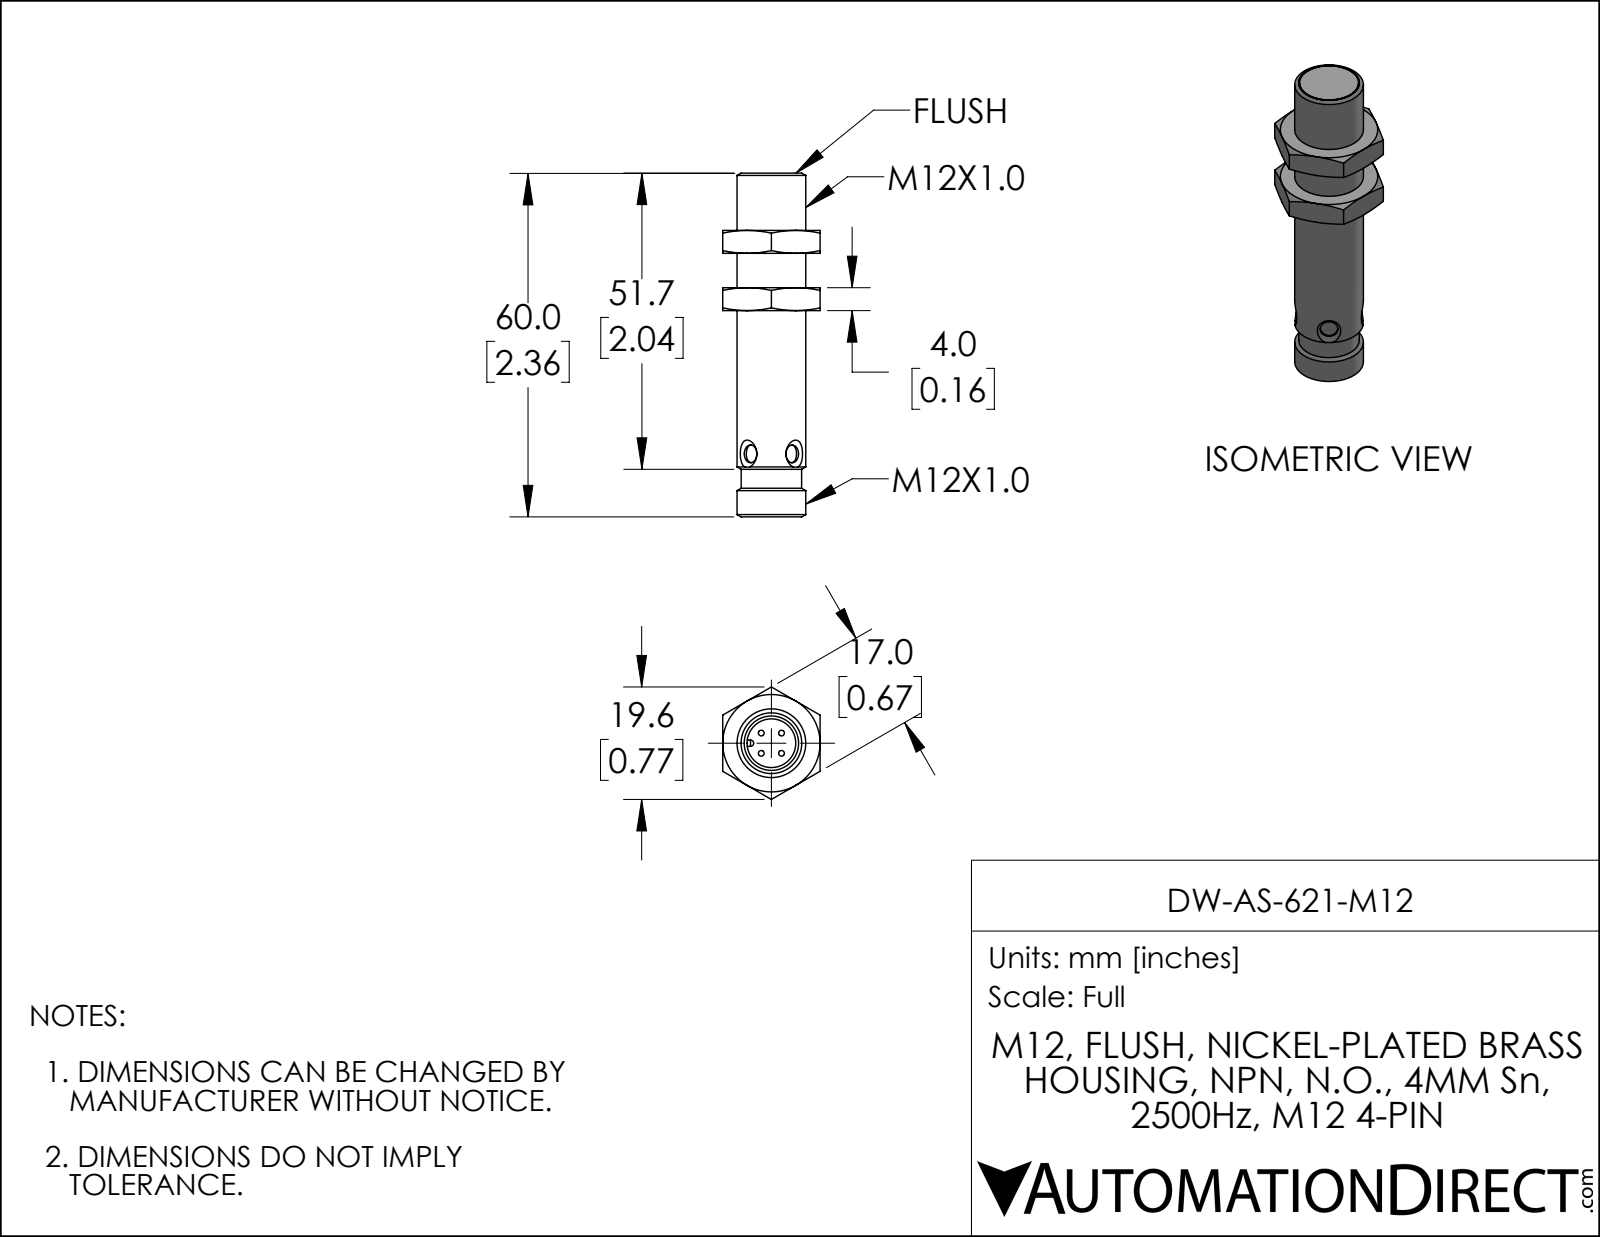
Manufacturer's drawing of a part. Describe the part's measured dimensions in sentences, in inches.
The part is named "DW-AS-621-M12". Its 3-D file was written by "SolidWorks 2019 (AUTOMOTIVE_DESIGN)". It is 1 solid with 83 faces: 23 planar, 22 cylindrical and 38 other. Overall it measures 2.362 by 0.773 by 0.669 inches. Its volume is 0.443 cubic inches and its surface area 5.45 square inches. Round holes: 2 of diameter 0.122, 1 of diameter 0.335, 1 of diameter 0.415. Round bosses or shafts: 4 of diameter 0.039, 1 of diameter 0.472, 1 of diameter 0.415, 1 of diameter 0.406. Partial cylindrical surfaces (rounded edges, fillets, slot ends): 2 of radius 0.022, 1 of radius 0.193. The main face-to-face distances are 0.394, 0.157, 0.669, 0.551, 0.236, 0.787, 0.945, 2.022, 1.629, 1.471.
